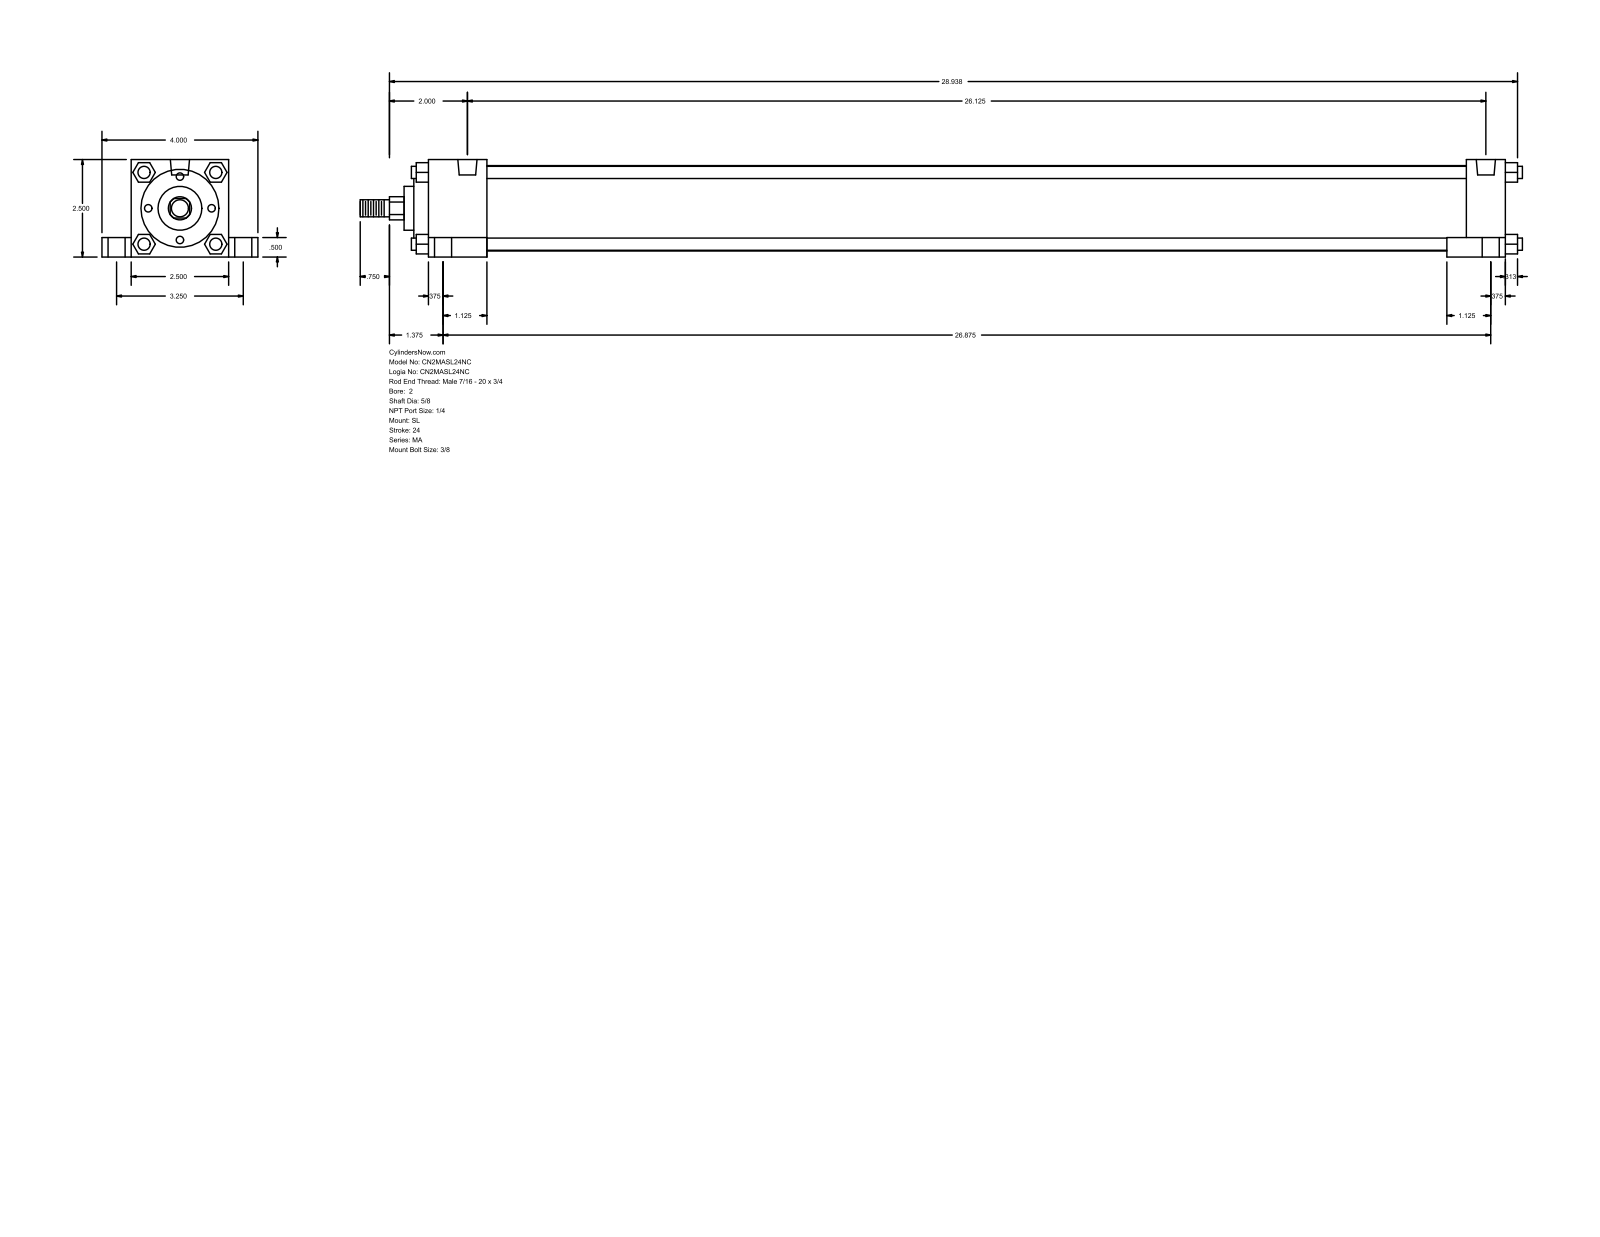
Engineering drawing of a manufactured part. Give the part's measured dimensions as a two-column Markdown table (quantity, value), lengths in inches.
| quantity | value |
| --- | --- |
| part name | MA_SL__0200_0.625 |
| STEP written by | GSSL Pune (CONFIG_CONTROL_DESIGN) |
| units | inches |
| bodies | 0 solids, 150 faces (113 planar, 37 cylindrical, 0 other) |
| overall size | 29.813 × 4 × 2.5 |
| round holes (diameter × count) | 0.313 × 4, 0.437 × 4, 0.687 × 4, 0.492 × 2 |
| round bosses / shafts (diameter × count) | 0.313 × 4, 2.19 × 1, 2 × 1, 1.125 × 1, 0.625 × 1, 0.437 × 1 |
| partial cylindrical surfaces (radius × count) | 0.297 × 1 |
| main face-to-face distances | 2.5, 0.5, 0.375, 25.125, 0.75, 3.25, 1.5, 2, 27.625, 26.125 |
| hole center spacings | 1.63, 1.741, 3.25, 26.125, 26.3, 26.8, 26.875, 27.071 |
